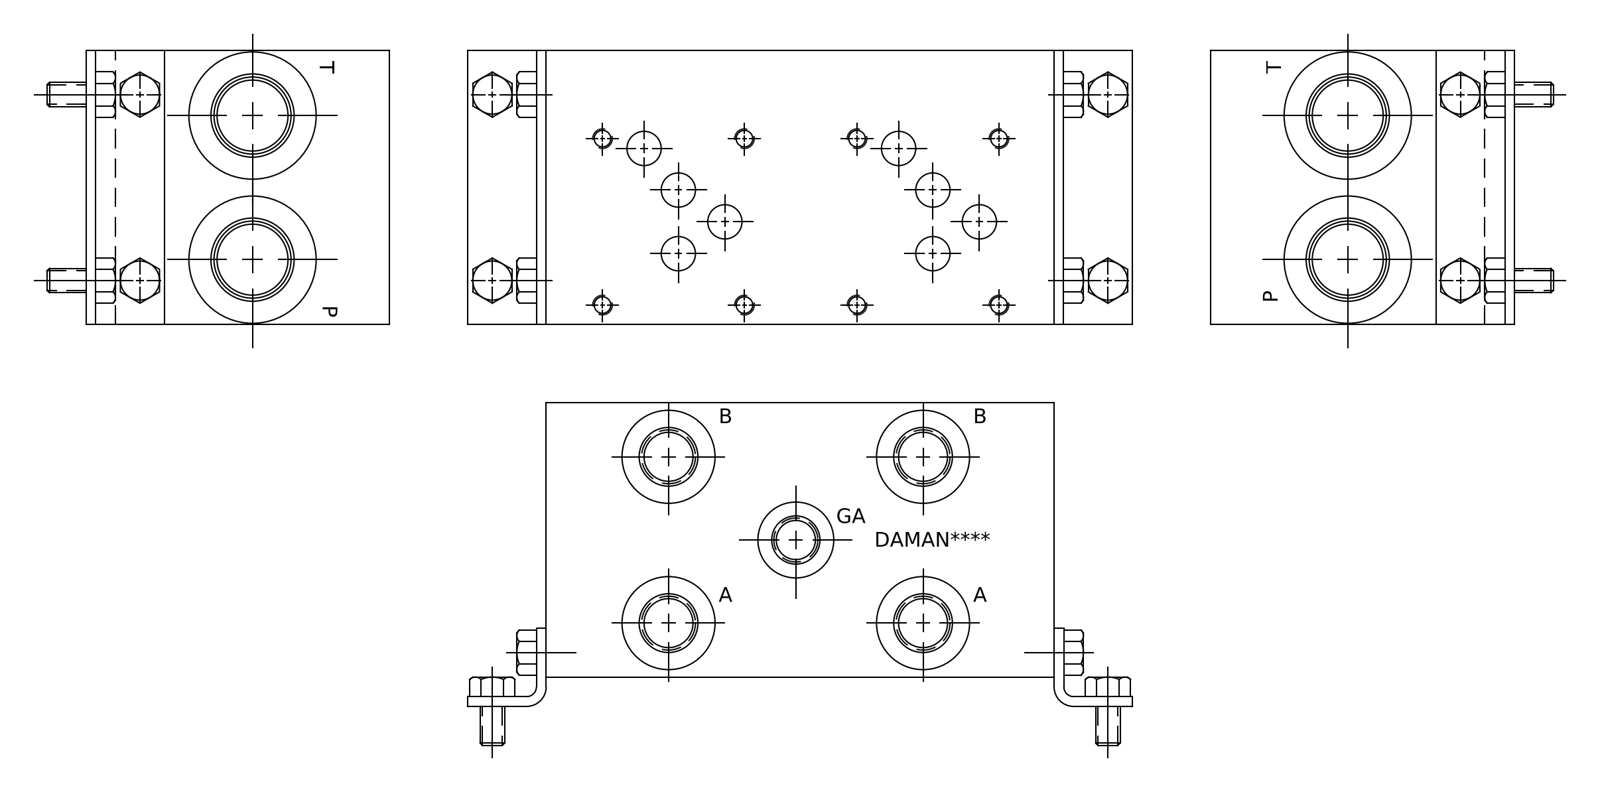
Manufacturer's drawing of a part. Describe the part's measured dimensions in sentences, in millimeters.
The part is named "Part_AD05P023S_3D". Its 3-D file was written by "Autodesk Inventor 2019 (AUTOMOTIVE_DESIGN)". It is 1 solid with 650 faces: 352 planar, 77 cylindrical and 221 other. Overall it measures 165.1 by 88.9 by 88.9 millimeters. Its volume is 1 190 000 cubic millimeters and its surface area 97 582 square millimeters. Round holes: 8 of diameter 5.11, 8 of diameter 6.35, 8 of diameter 11.13, 4 of diameter 15.88, 4 of diameter 17.5, 4 of diameter 19.05, 4 of diameter 19.25, 4 of diameter 30.63, 2 of diameter 6.53, 2 of diameter 7.92, 2 of diameter 23.01, 2 of diameter 24.92. The main face-to-face distances are 88.9, 165.1, 0.79, 164.31, 88.11, 163.52, 19.05, 19.84, 145.26, 144.47. The hole center spacings are 82.55, 46.05, 70.95, 98.63, 29.74, 53.98, 13.88, 18.27.
